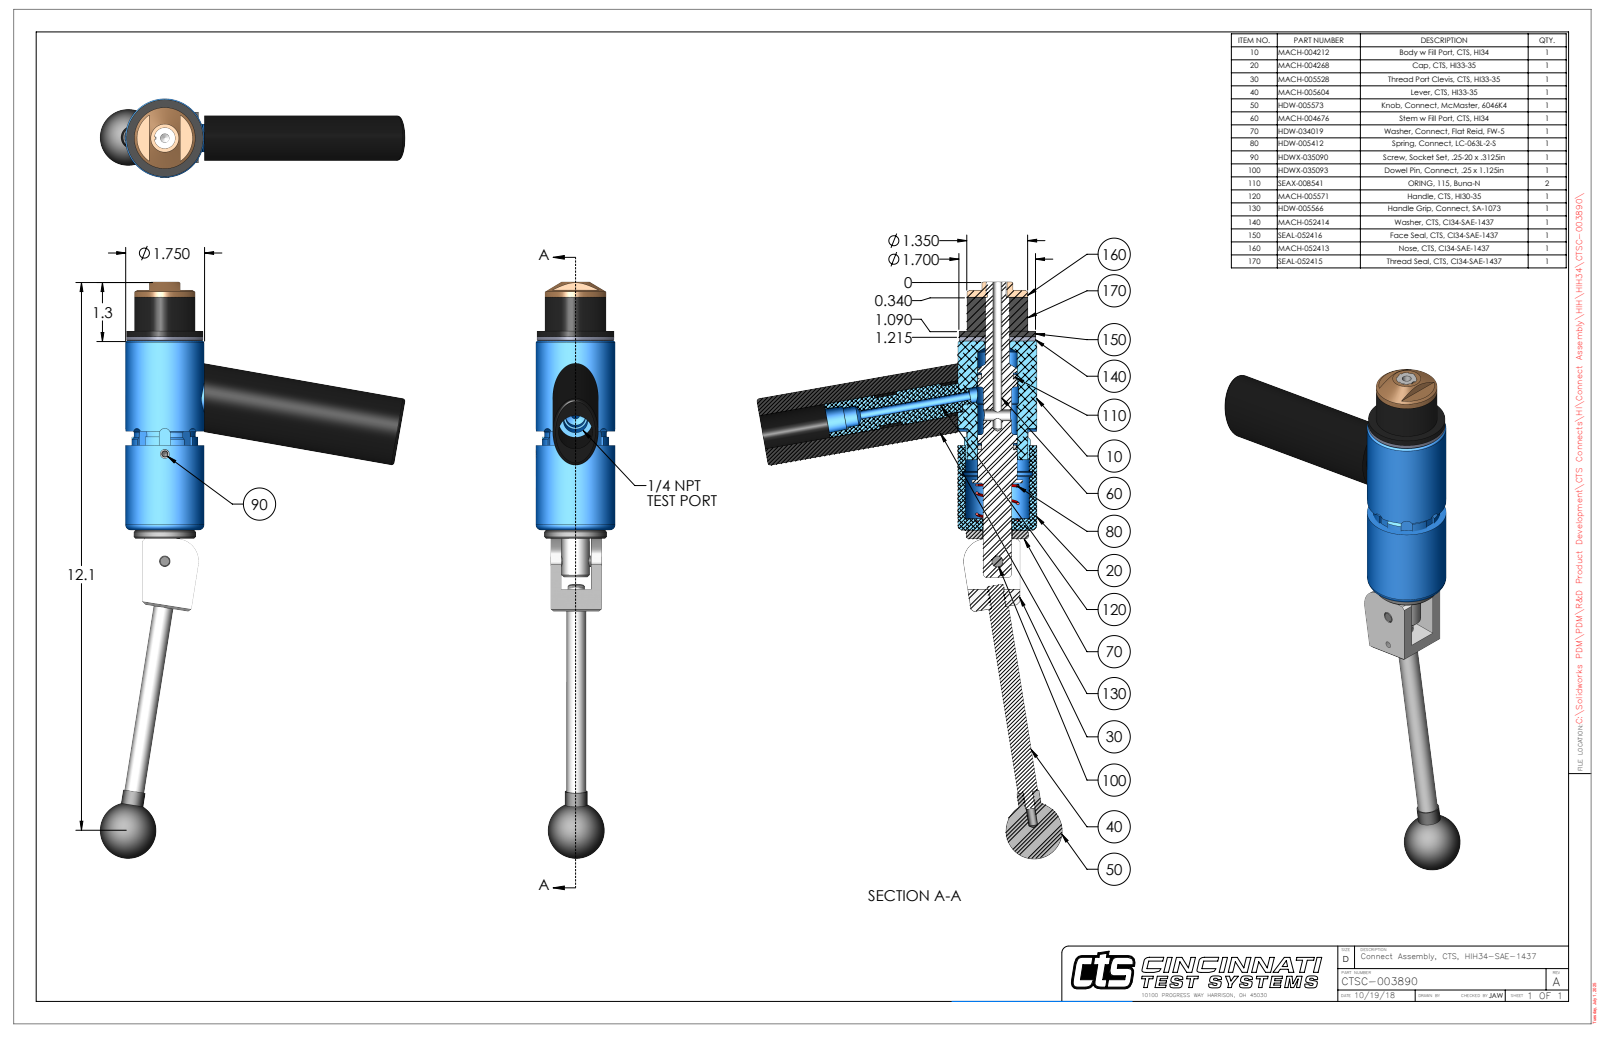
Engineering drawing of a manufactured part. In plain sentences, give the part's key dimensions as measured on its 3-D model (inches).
The part is named "CTSC-003890". Its 3-D file was written by "SolidWorks 2023 (AUTOMOTIVE_DESIGN)". It is 11 solids with 333 faces: 118 planar, 144 cylindrical and 71 other. Overall it measures 12.773 by 6.763 by 1.75 inches. Its volume is 19.2 cubic inches and its surface area 124.1 square inches. Round holes: 2 of diameter 0.201, 1 of diameter 0.15, 1 of diameter 0.187, 1 of diameter 0.204, 1 of diameter 0.249, 1 of diameter 0.25, 1 of diameter 0.251, 1 of diameter 0.313, 1 of diameter 0.422, 1 of diameter 0.438, 1 of diameter 0.53, 1 of diameter 0.547. Round bosses or shafts: 2 of diameter 0.5, 2 of diameter 0.44, 2 of diameter 0.25, 1 of diameter 1.75, 1 of diameter 1.7, 1 of diameter 1.38, 1 of diameter 1.35, 1 of diameter 0.75. Partial cylindrical surfaces (rounded edges, fillets, slot ends): 4 of radius 0.125, 2 of radius 0.029, 1 of radius 0.166, 1 of radius 0.166, 1 of radius 0.187, 1 of radius 0.33, 1 of radius 0.5, 1 of radius 0.695. The main face-to-face distances are 0.094, 0.219, 0.125, 0.75, 0.875, 0.969, 5.158, 4.408, 4.283, 4.189. The hole center spacings are 0.74, 2.376, 3.116.
